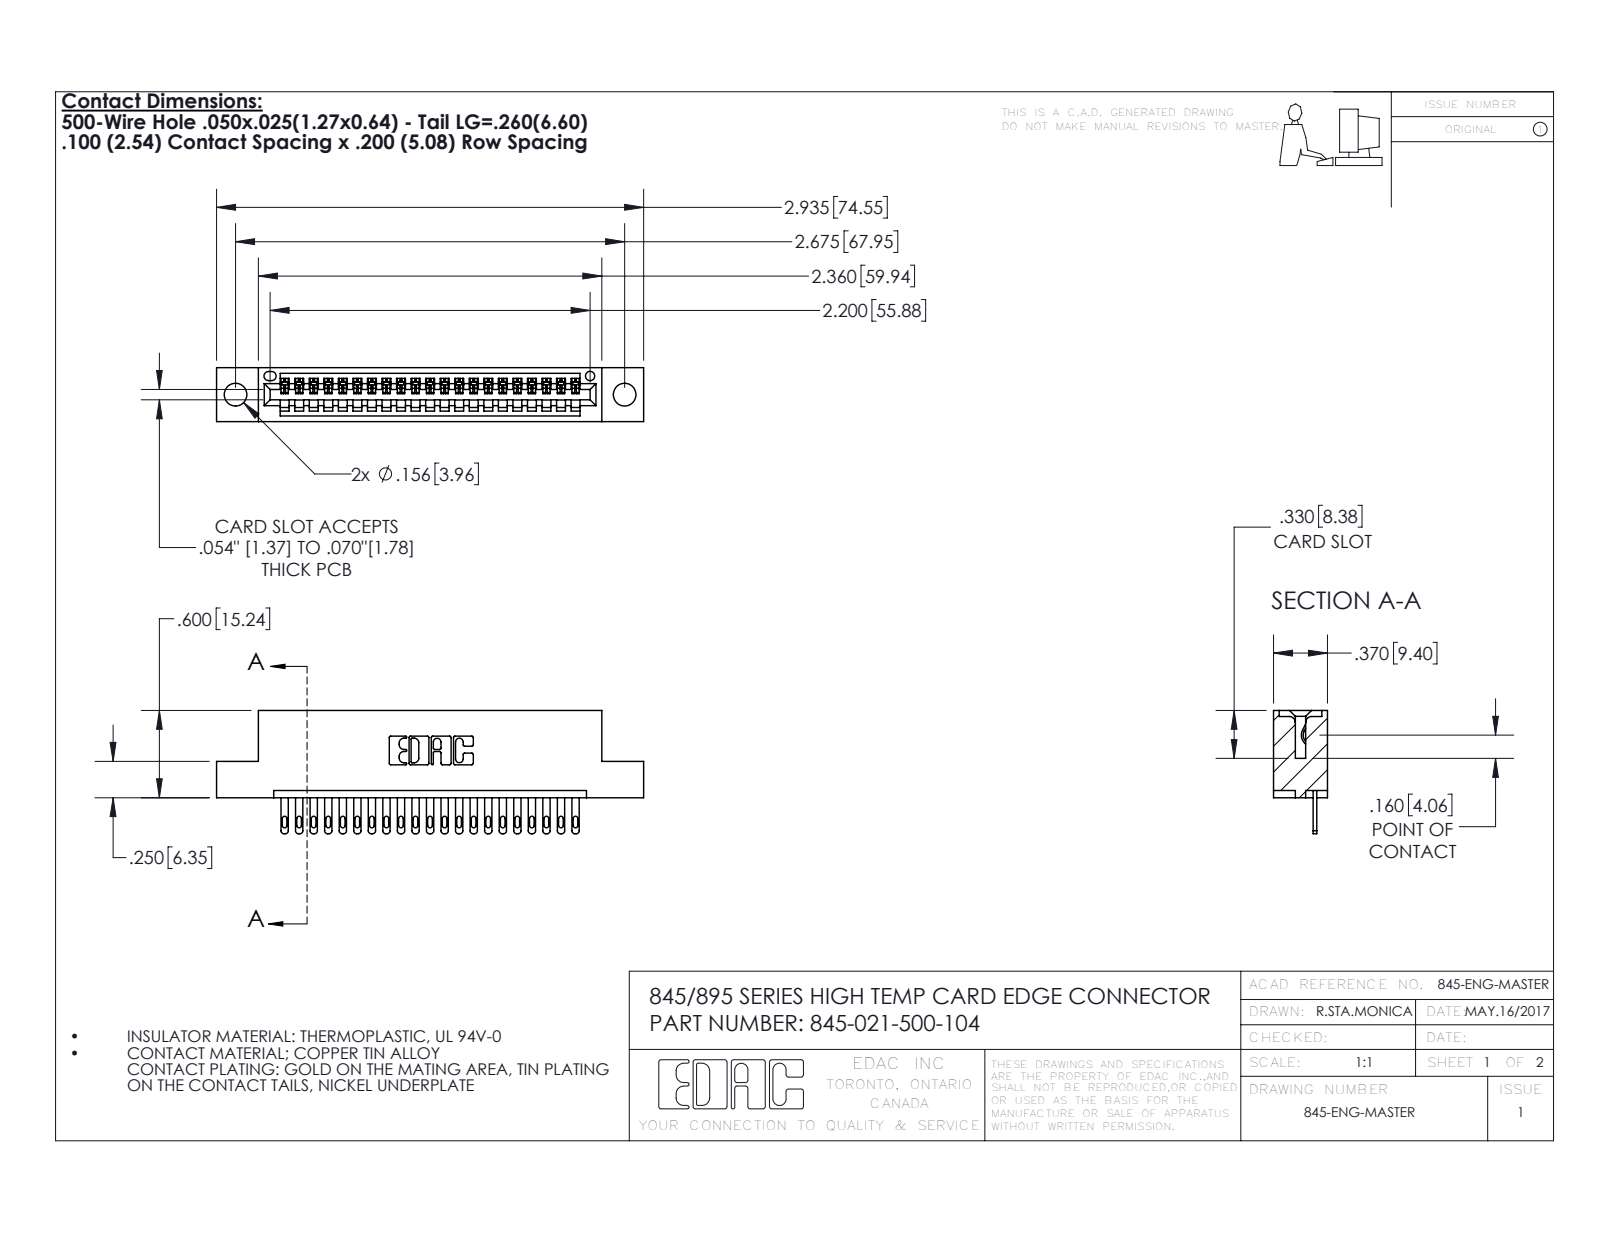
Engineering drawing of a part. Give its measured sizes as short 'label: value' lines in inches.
name: 345-021-500-104; 345 Part_Flush Mounting Lugs - 0.156 Dia-TH; 345-292-001_345-293-100
written by: SolidWorks 2016 (CONFIG_CONTROL_DESIGN)
unit: in
bodies: 22 solids, 1260 faces (794 planar, 466 cylindrical, 0 other)
size: 2.935 × 0.847 × 0.37
volume: 0.417 in³; area: 13.41 in²
holes: 2× ⌀0.156, 1× ⌀0.064
rounds: 42× R0.006, 42× R0.016, 42× R0.02, 22× R0.01, 6× R0.007, 6× R0.031, 3× R0.026, 2× R0.031
face distances: 0.298, 0.072, 0.2, 0.37, 0.098, 0.272, 0.025, 0.225, 0.149, 0.072
hole spacings: 0.27, 2.441, 2.675
